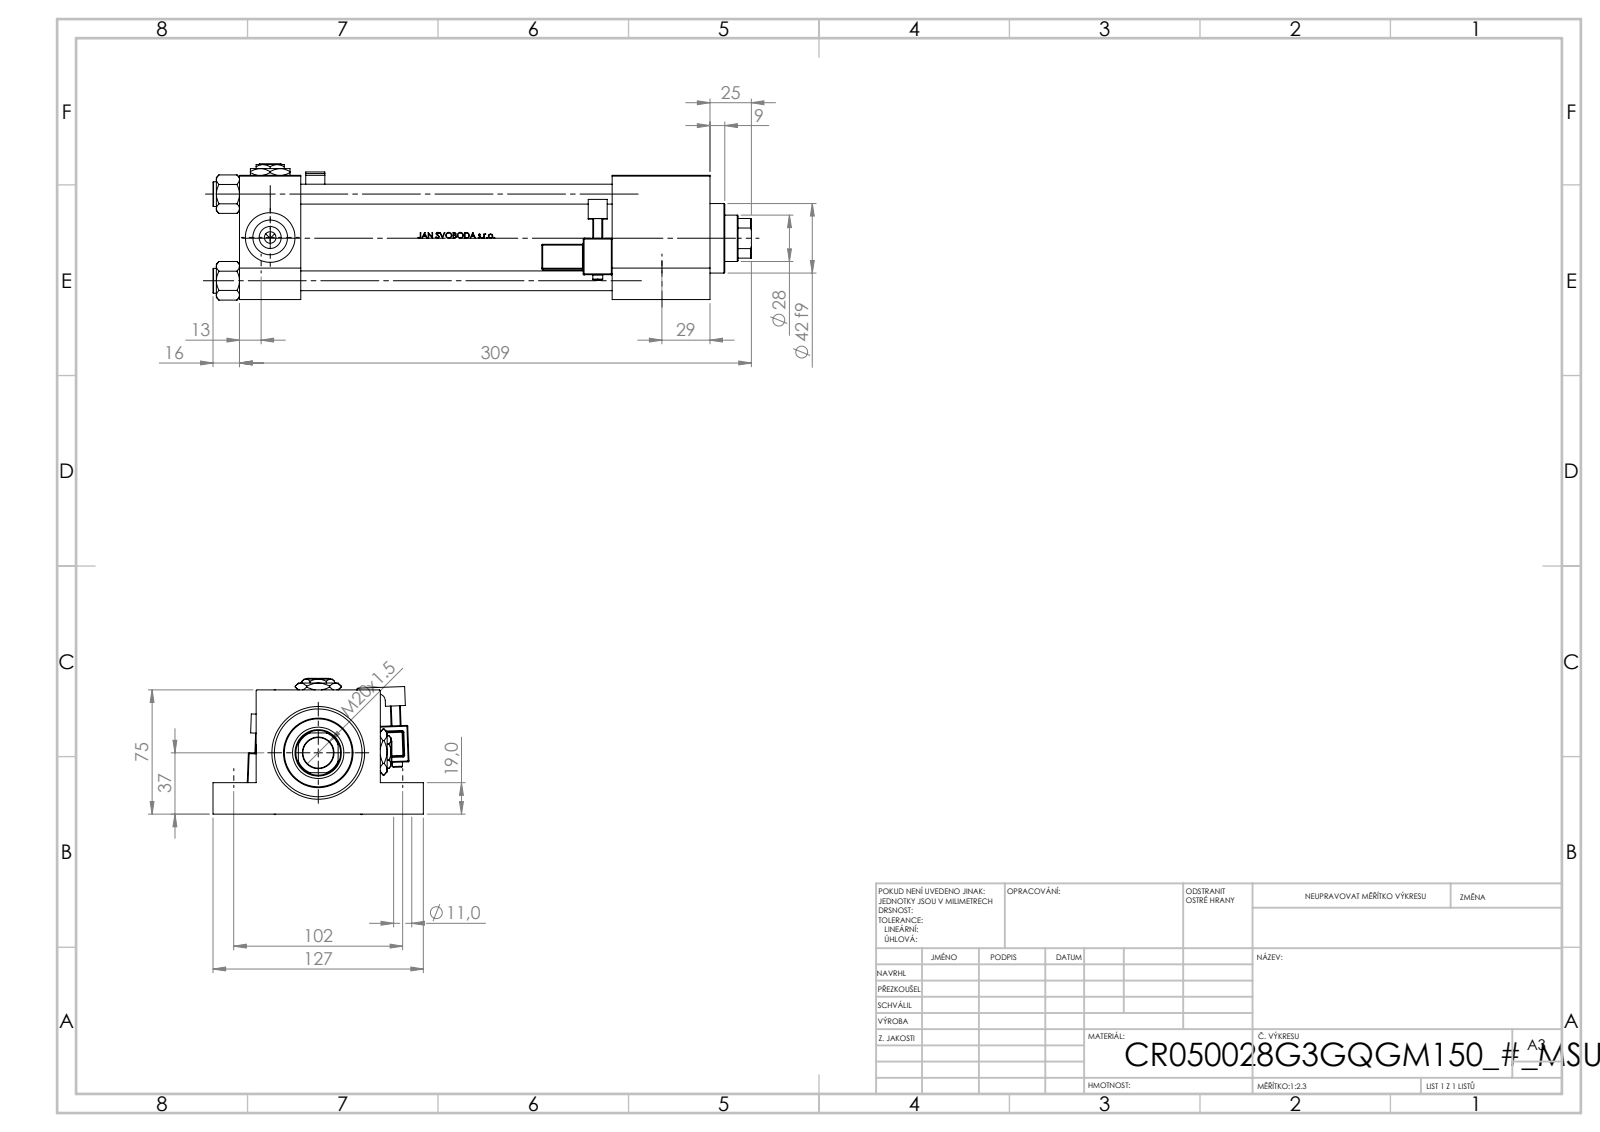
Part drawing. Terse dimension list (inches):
name: V215CR_MSU; NUT_M5_G; V215CR_G_TYCINKA; V215CR_G_Body (+3 more)
written by: SolidWorks 2019 (CONFIG_CONTROL_DESIGN)
unit: in
bodies: 19 solids, 1417 faces (556 planar, 203 cylindrical, 658 other)
size: 12.795 × 5 × 3.239
volume: 65.48 in³; area: 430.2 in²
holes: 4× ⌀0.472, 4× ⌀0.551, 3× ⌀0.276, 3× ⌀0.825, 3× ⌀1.181, 1× ⌀0.728, 1× ⌀1.102, 1× ⌀1.22, 1× ⌀1.614, 1× ⌀1.969, 1× ⌀2.087
bosses: 4× ⌀0.591, 2× ⌀0.236, 1× ⌀2.205, 1× ⌀1.654
rounds: 48× R0.02, 2× R0.039, 2× R0.098, 2× R0.157, 1× R0.531
face distances: 2.953, 1.457, 11.181, 9.724, 8.858, 7.402, 2.323, 2.205, 0.748, 1.024
hole spacings: 1.456, 2.059, 2.02, 2.912, 4.016, 9.525, 9.528, 10.339
